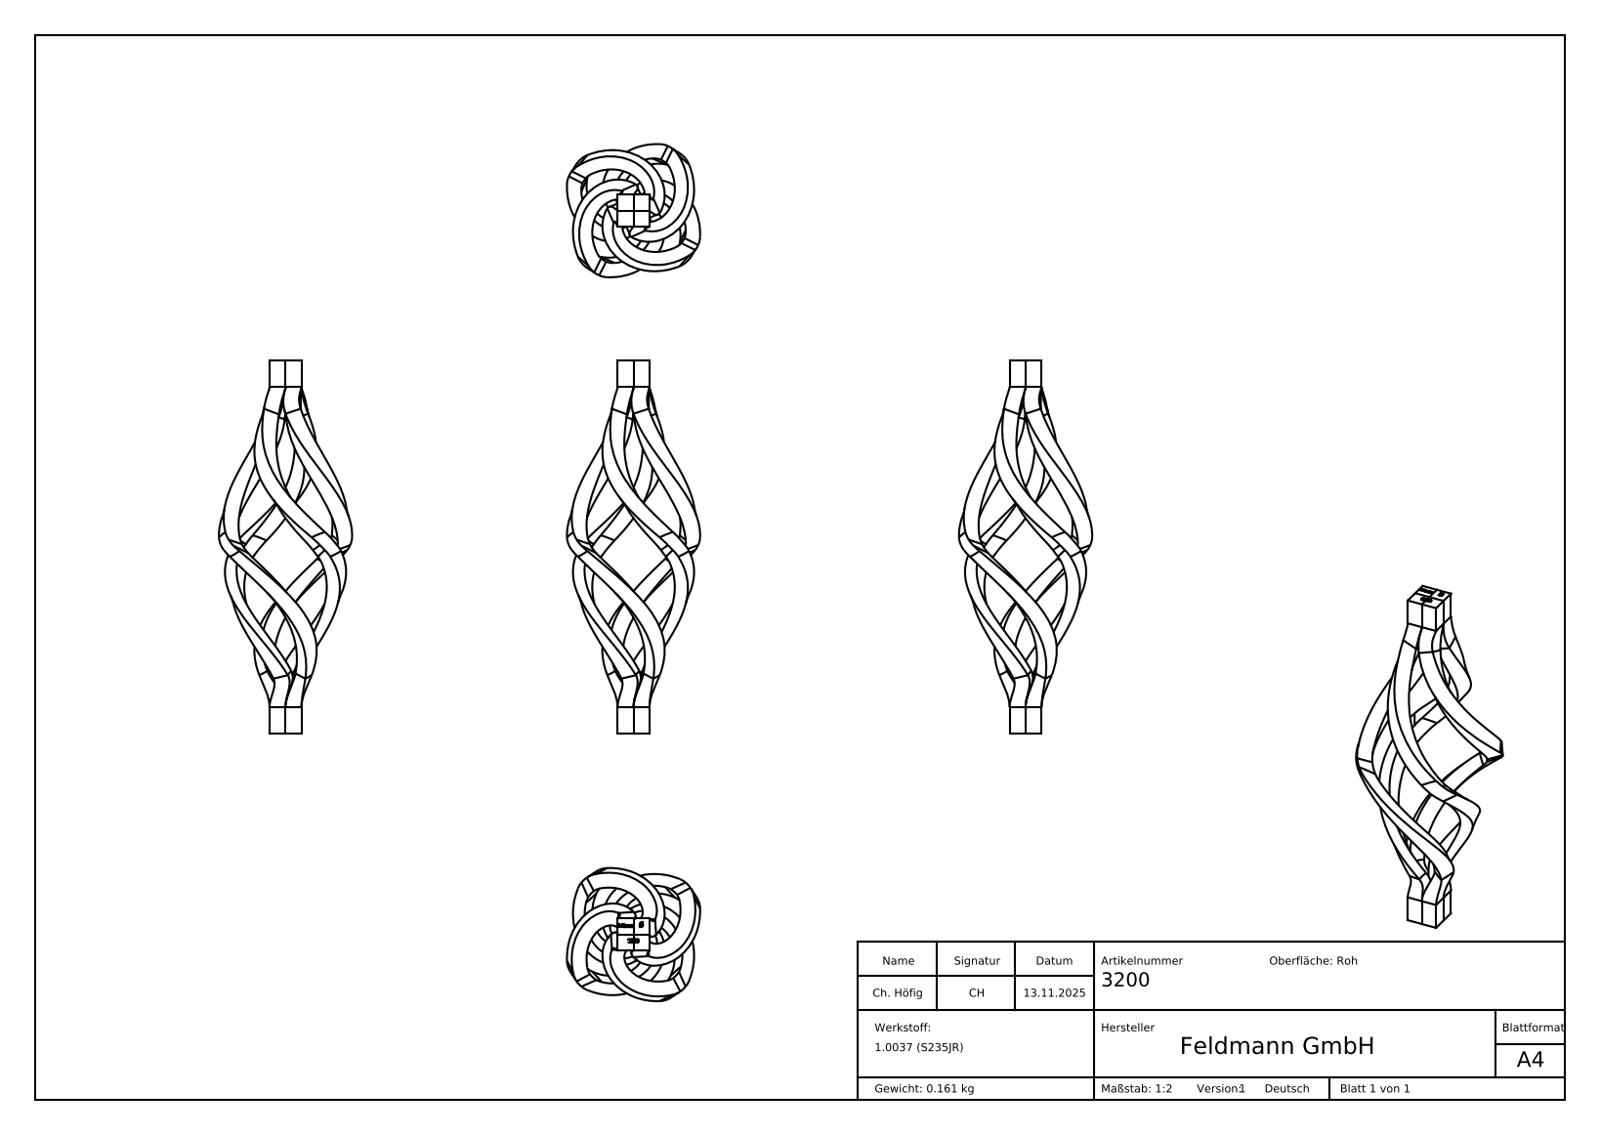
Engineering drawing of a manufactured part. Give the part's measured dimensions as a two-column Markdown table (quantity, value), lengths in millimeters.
| quantity | value |
| --- | --- |
| part name | 3200 |
| STEP written by | SolidWorks 2018 (CONFIG_CONTROL_DESIGN) |
| units | millimeters |
| bodies | 4 solids, 329 faces (143 planar, 0 cylindrical, 186 other) |
| overall size | 140 × 50 × 50 |
| volume | 20 593 mm³ |
| surface area | 15 298 mm² |
| main face-to-face distances | 6, 12, 140, 139.9, 3, 9, 1.1, 0.83, 0.76, 7.13 |
